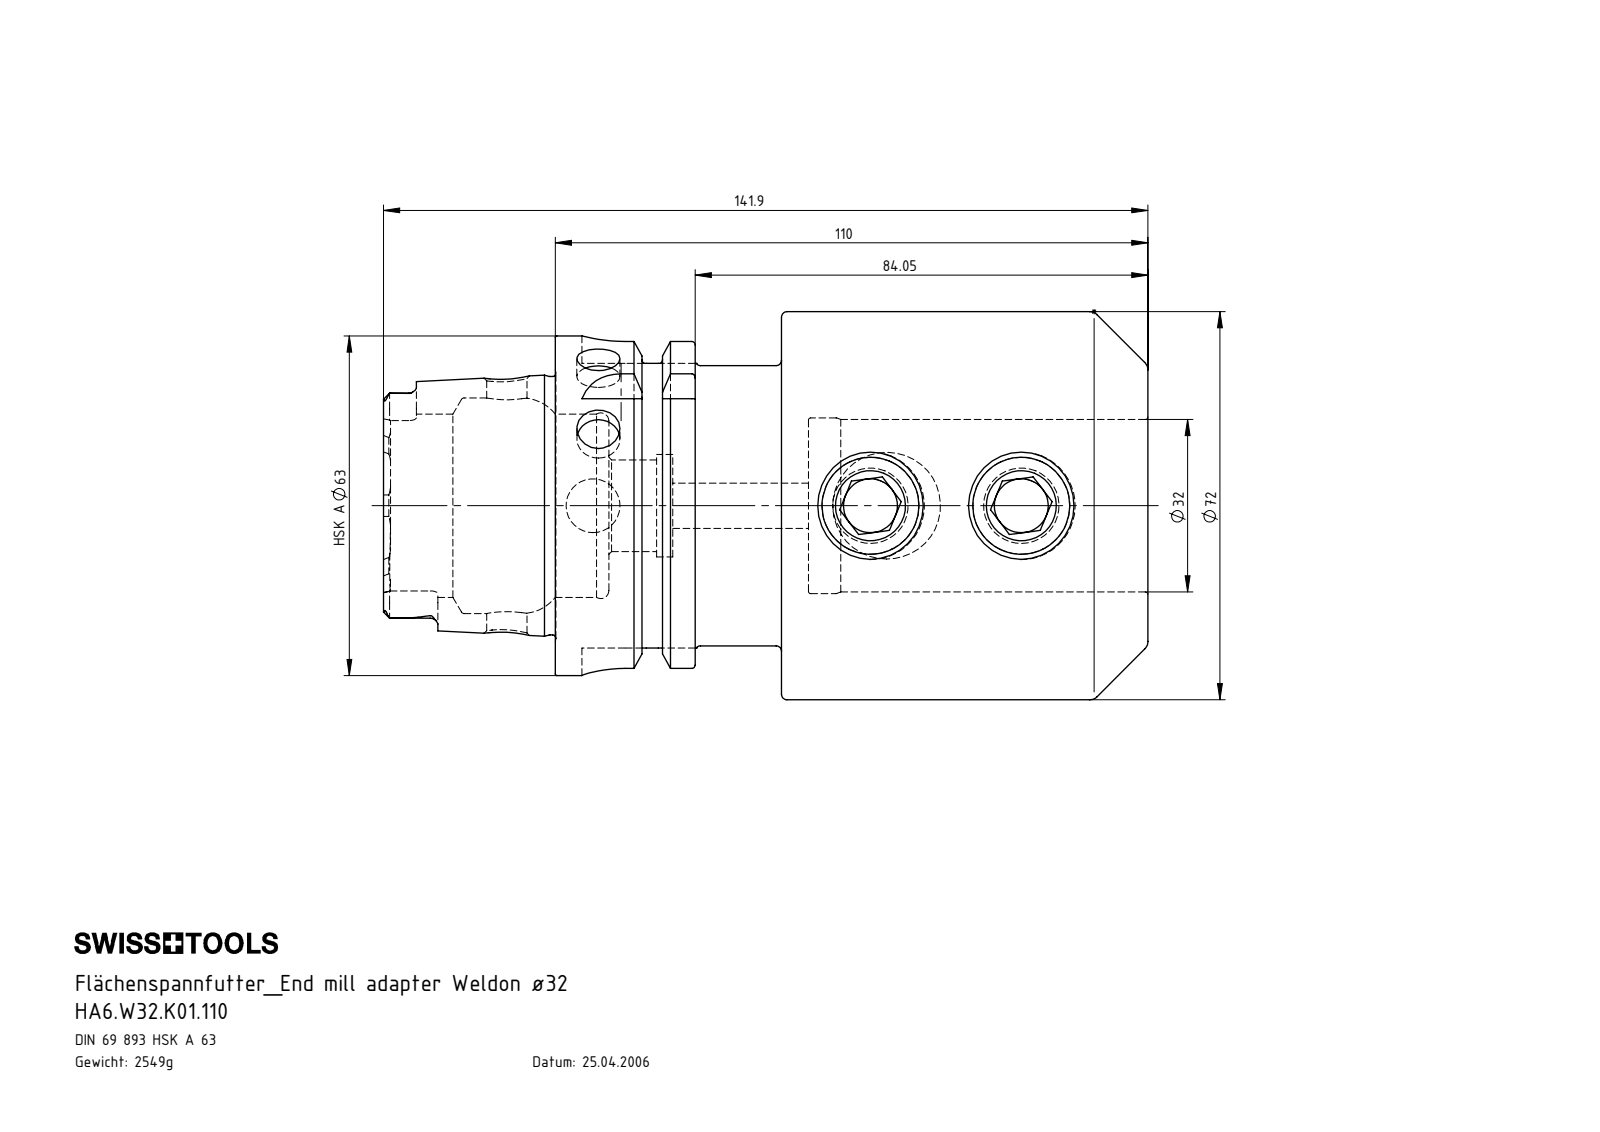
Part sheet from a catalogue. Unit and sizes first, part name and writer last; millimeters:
Units: millimetres
Overall size (bounding box): 141.9 × 72 × 72
Round holes (diameter × count): ⌀8 ×2, ⌀18 ×2, ⌀7.5 ×1, ⌀8.4 ×1, ⌀10 ×1, ⌀17 ×1, ⌀19 ×1, ⌀32 ×1, ⌀32.6 ×1, ⌀34 ×1, ⌀40 ×1
Round bosses / shafts (diameter × count): ⌀20 ×2, ⌀72 ×1, ⌀63 ×1, ⌀54.95 ×1, ⌀52 ×1, ⌀47.94 ×1
Partial cylindrical surfaces — rounded edges, fillets, slot ends (radius × count): R1.4 ×6, R2.88 ×4, R8 ×4
Main face-to-face distances: 68, 42, 110, 5, 47, 63, 25.95, 16.05, 21.05, 84.05
Hole centre spacings: 28, 51.5, 79.5
Volume: 324 664 mm³ · Surface area: 55 740 mm²
Bodies: 3 solids, 261 faces (79 planar, 63 cylindrical, 119 other)
Part name (STEP PRODUCT): HA6.W32.K01.110; W32-ER1.001.020; HA6-W32.K01.110_C_Fertigbearbeitung
STEP written by: SolidWorks 2012 (CONFIG_CONTROL_DESIGN)
